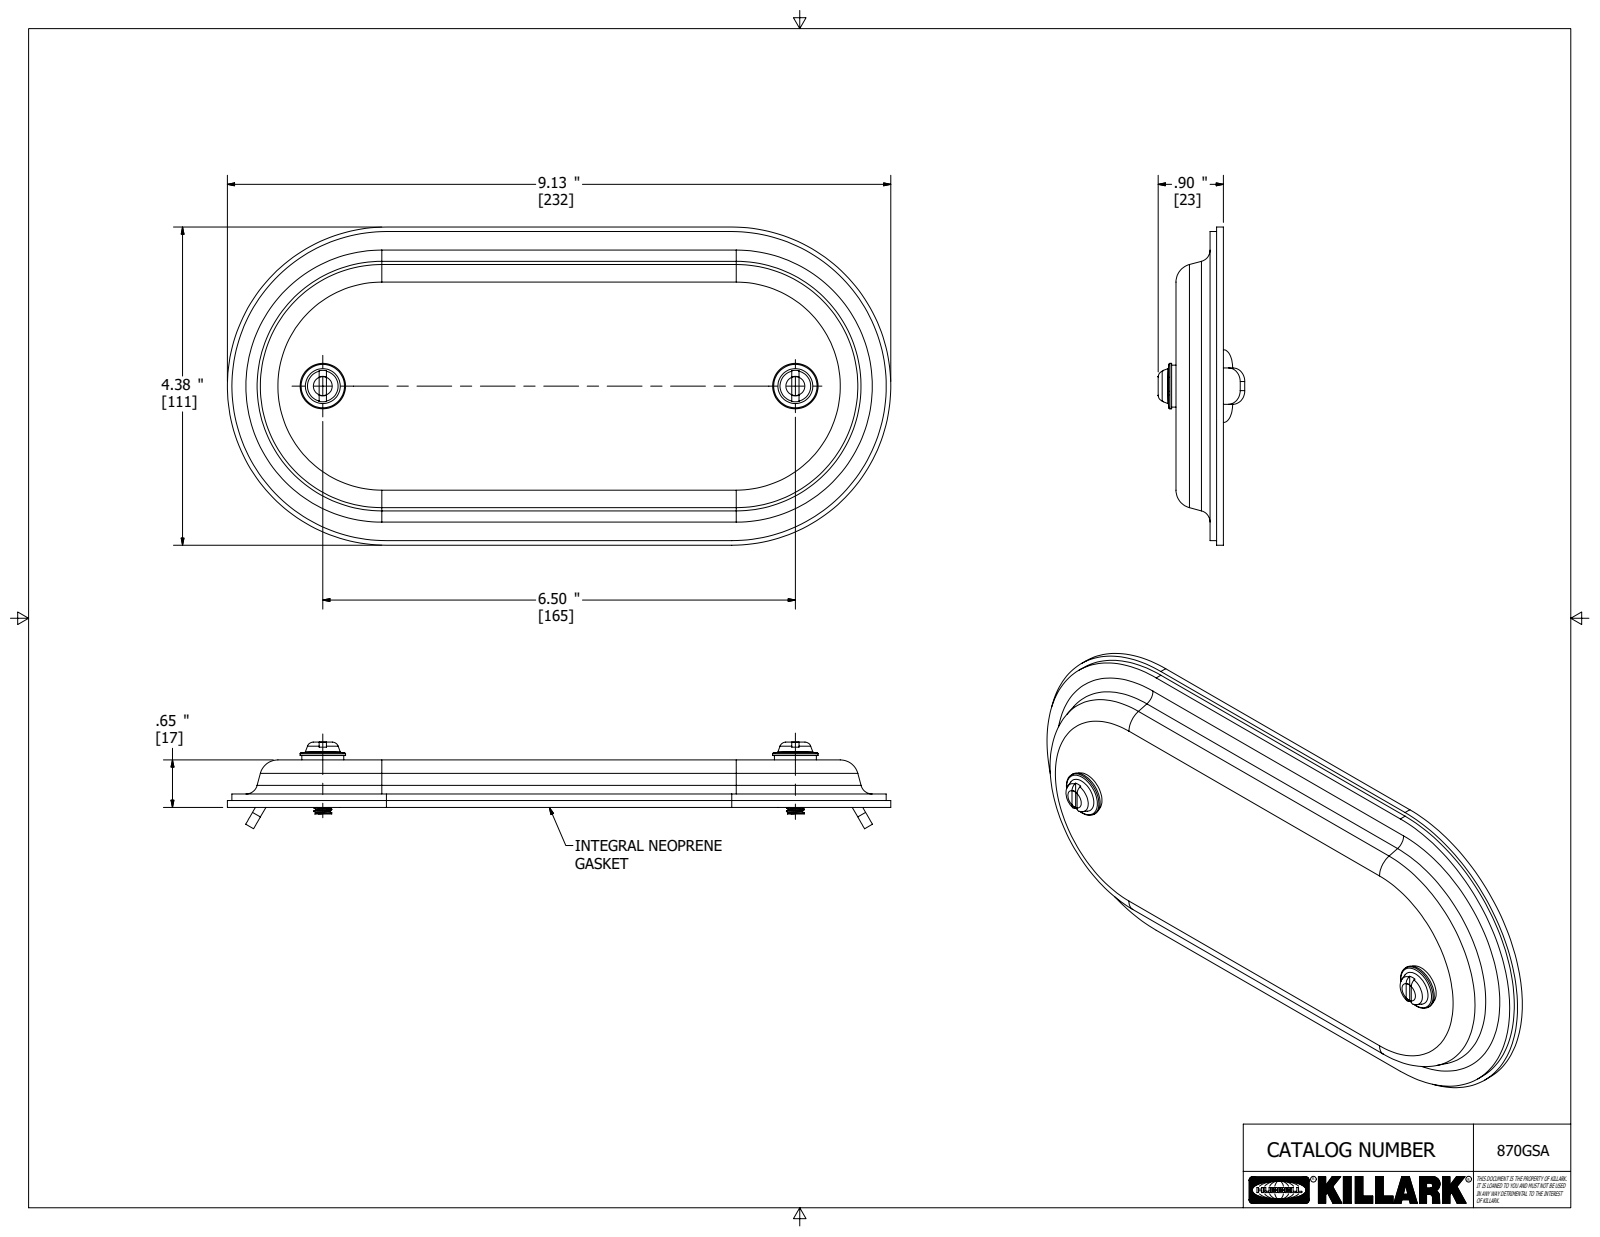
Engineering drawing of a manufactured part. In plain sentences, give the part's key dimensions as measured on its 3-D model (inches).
The part is named "870GSA; 870SA; 17733; 18038CABB (+2 more)". Its 3-D file was written by "Autodesk Inventor 2018 (AUTOMOTIVE_DESIGN)". It is 6 solids with 210 faces: 102 planar, 80 cylindrical and 28 other. Overall it measures 9.125 by 4.375 by 1.191 inches. Its volume is 7.694 cubic inches and its surface area 171.4 square inches. Round holes: 2 of diameter 0.25, 2 of diameter 0.344. Round bosses or shafts: 2 of diameter 0.625, 2 of diameter 0.577, 2 of diameter 0.246, 2 of diameter 0.196. Partial cylindrical surfaces (rounded edges, fillets, slot ends): 28 of radius 0.125, 8 of radius 0.187, 8 of radius 0.25, 4 of radius 0.16, 4 of radius 0.5, 4 of radius 0.875, 2 of radius 0.219, 2 of radius 1.75. The main face-to-face distances are 0.094, 0.09, 0.563, 0.469, 0.652, 0.559, 0.125, 0.469, 0.184, 0.09. The hole center spacings are 6.5, 6.5, 6.5.
